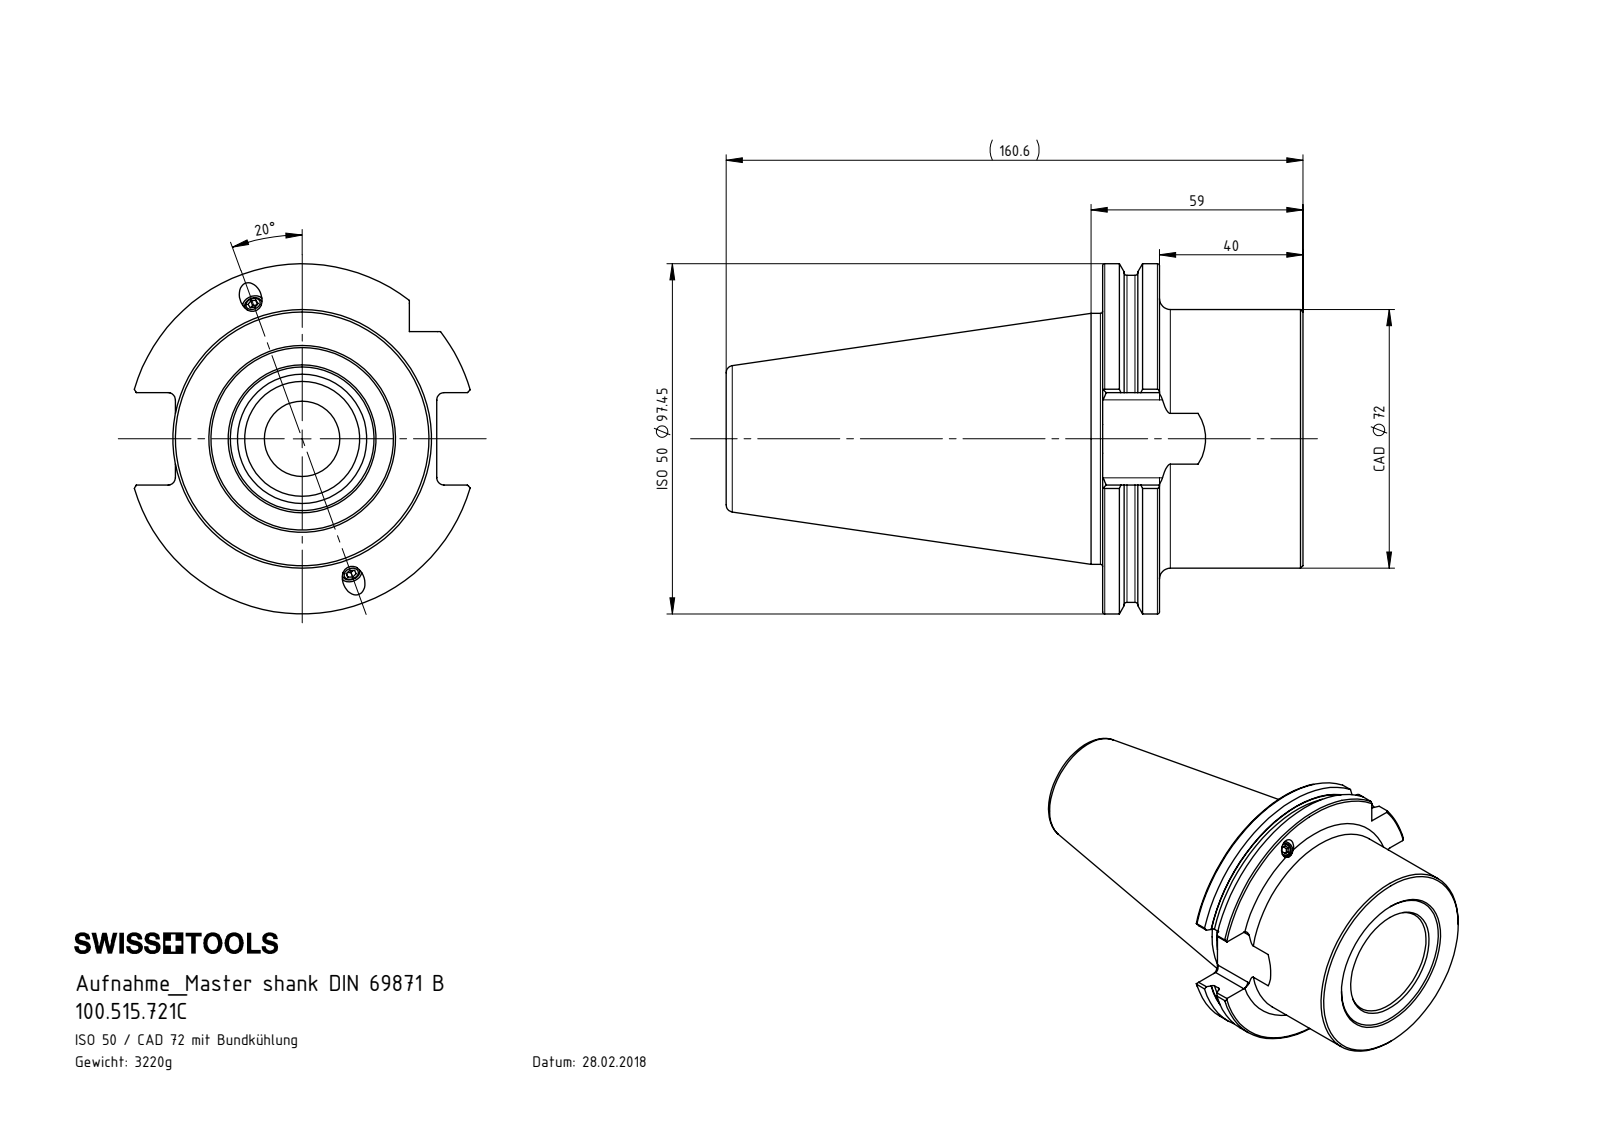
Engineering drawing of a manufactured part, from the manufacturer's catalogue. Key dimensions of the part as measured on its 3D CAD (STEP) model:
Part name (STEP PRODUCT): ISO 4026 - M5 x 5; 100.515.721C; SB5-CA7.K01.059_A_mit Bundkhlung
STEP written by: SolidWorks 2017 (CONFIG_CONTROL_DESIGN)
Units: millimetres
Bodies: 5 solids, 217 faces (70 planar, 66 cylindrical, 81 other)
Overall size (bounding box): 160.6 × 97.45 × 93.51
Volume: 410 231 mm³ · Surface area: 59 482 mm²
Round holes (diameter × count): ⌀4.2 ×4, ⌀6 ×4, ⌀21 ×1, ⌀25 ×1, ⌀25.45 ×1, ⌀32 ×1, ⌀40 ×1, ⌀40.6 ×1
Round bosses / shafts (diameter × count): ⌀5 ×4, ⌀91 ×1, ⌀72 ×1, ⌀69.85 ×1
Partial cylindrical surfaces — rounded edges, fillets, slot ends (radius × count): R2 ×8, R12.85 ×1, R48.73 ×1
Main face-to-face distances: 15.85, 55.8, 39.95, 55.2, 39.35, 0.6, 104.8, 120.65, 160, 160.6
